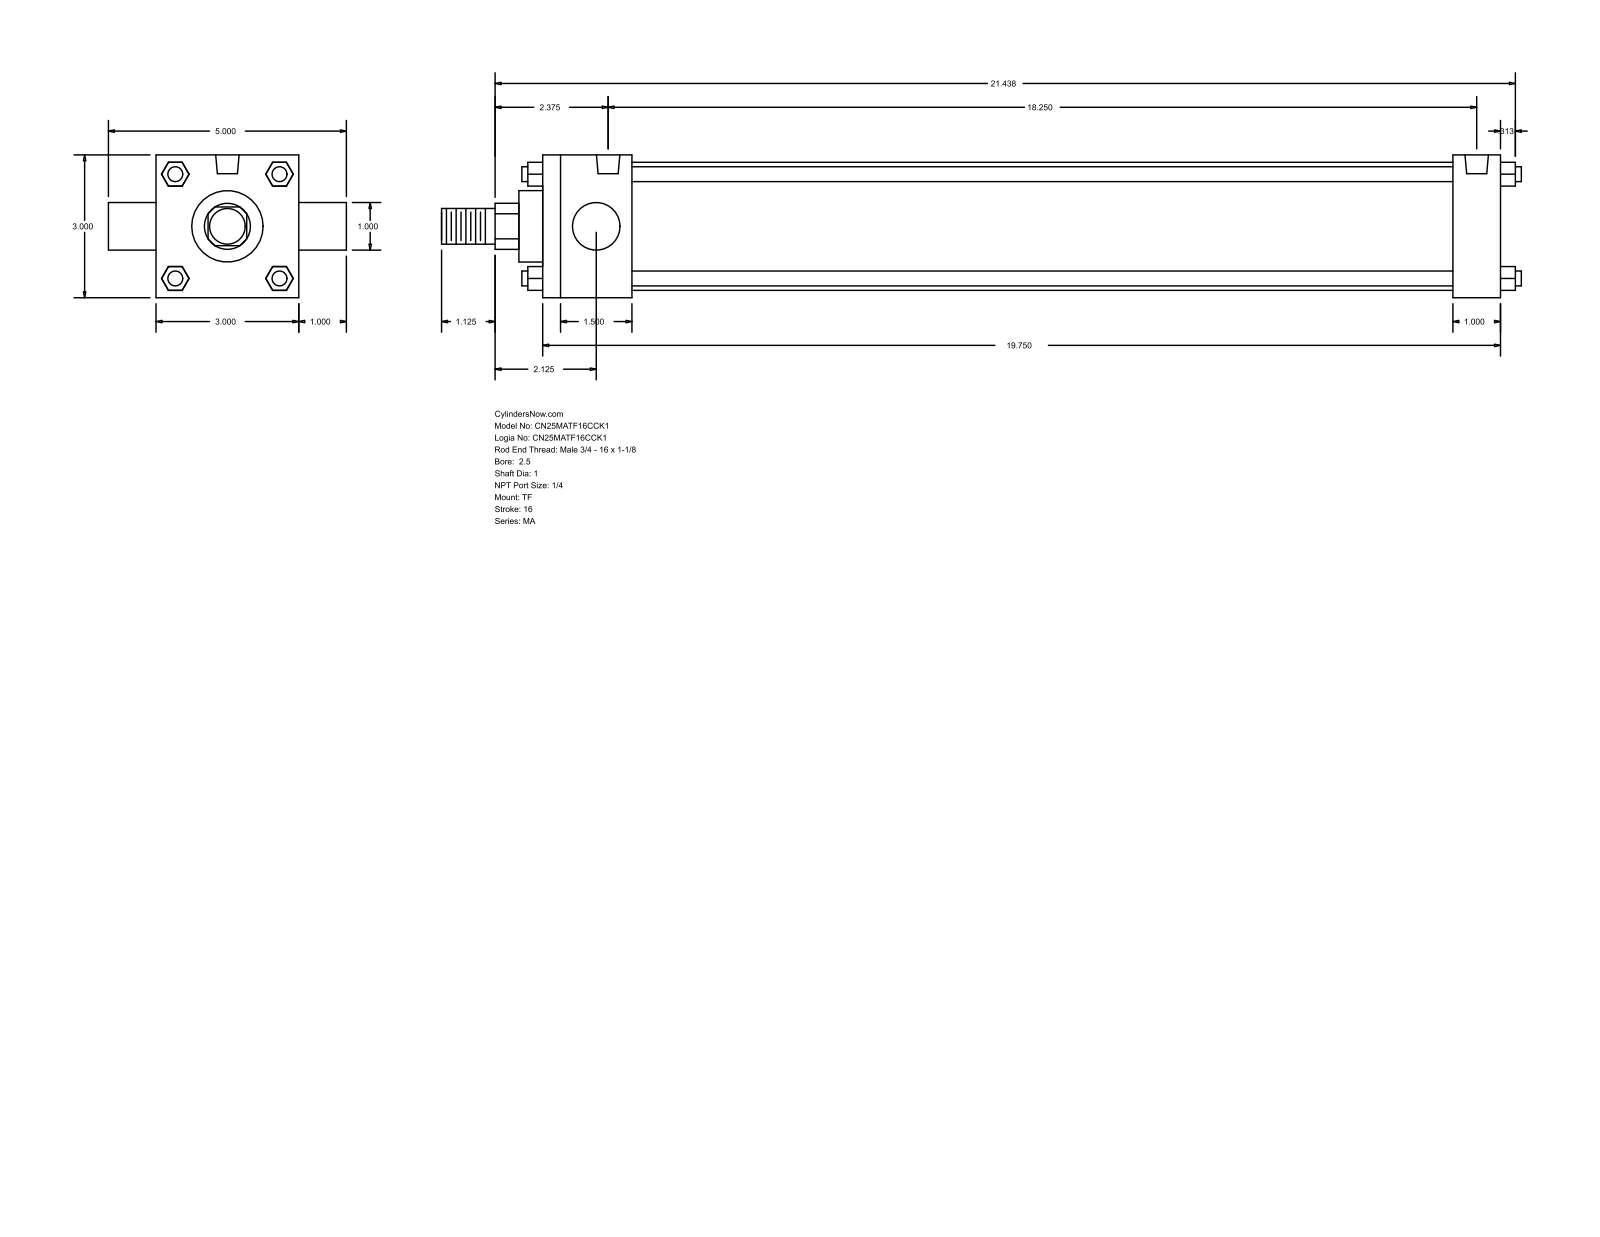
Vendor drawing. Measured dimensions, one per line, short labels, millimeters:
name: MA_TF__0250_1
written by: GSSL Pune (CONFIG_CONTROL_DESIGN)
unit: mm
bodies: 0 solids, 120 faces (92 planar, 28 cylindrical, 0 other)
size: 576.26 × 127 × 76.2
holes: 3× ⌀7.94, 2× ⌀12.49
bosses: 4× ⌀7.94, 2× ⌀25.4, 1× ⌀68.33, 1× ⌀38.1, 1× ⌀19.05
rounds: 1× R12.29
face distances: 76.2, 511.18, 25.4, 12.7, 47.63, 485.78, 438.15, 463.55, 101.6, 27.81
hole spacings: 463.55
